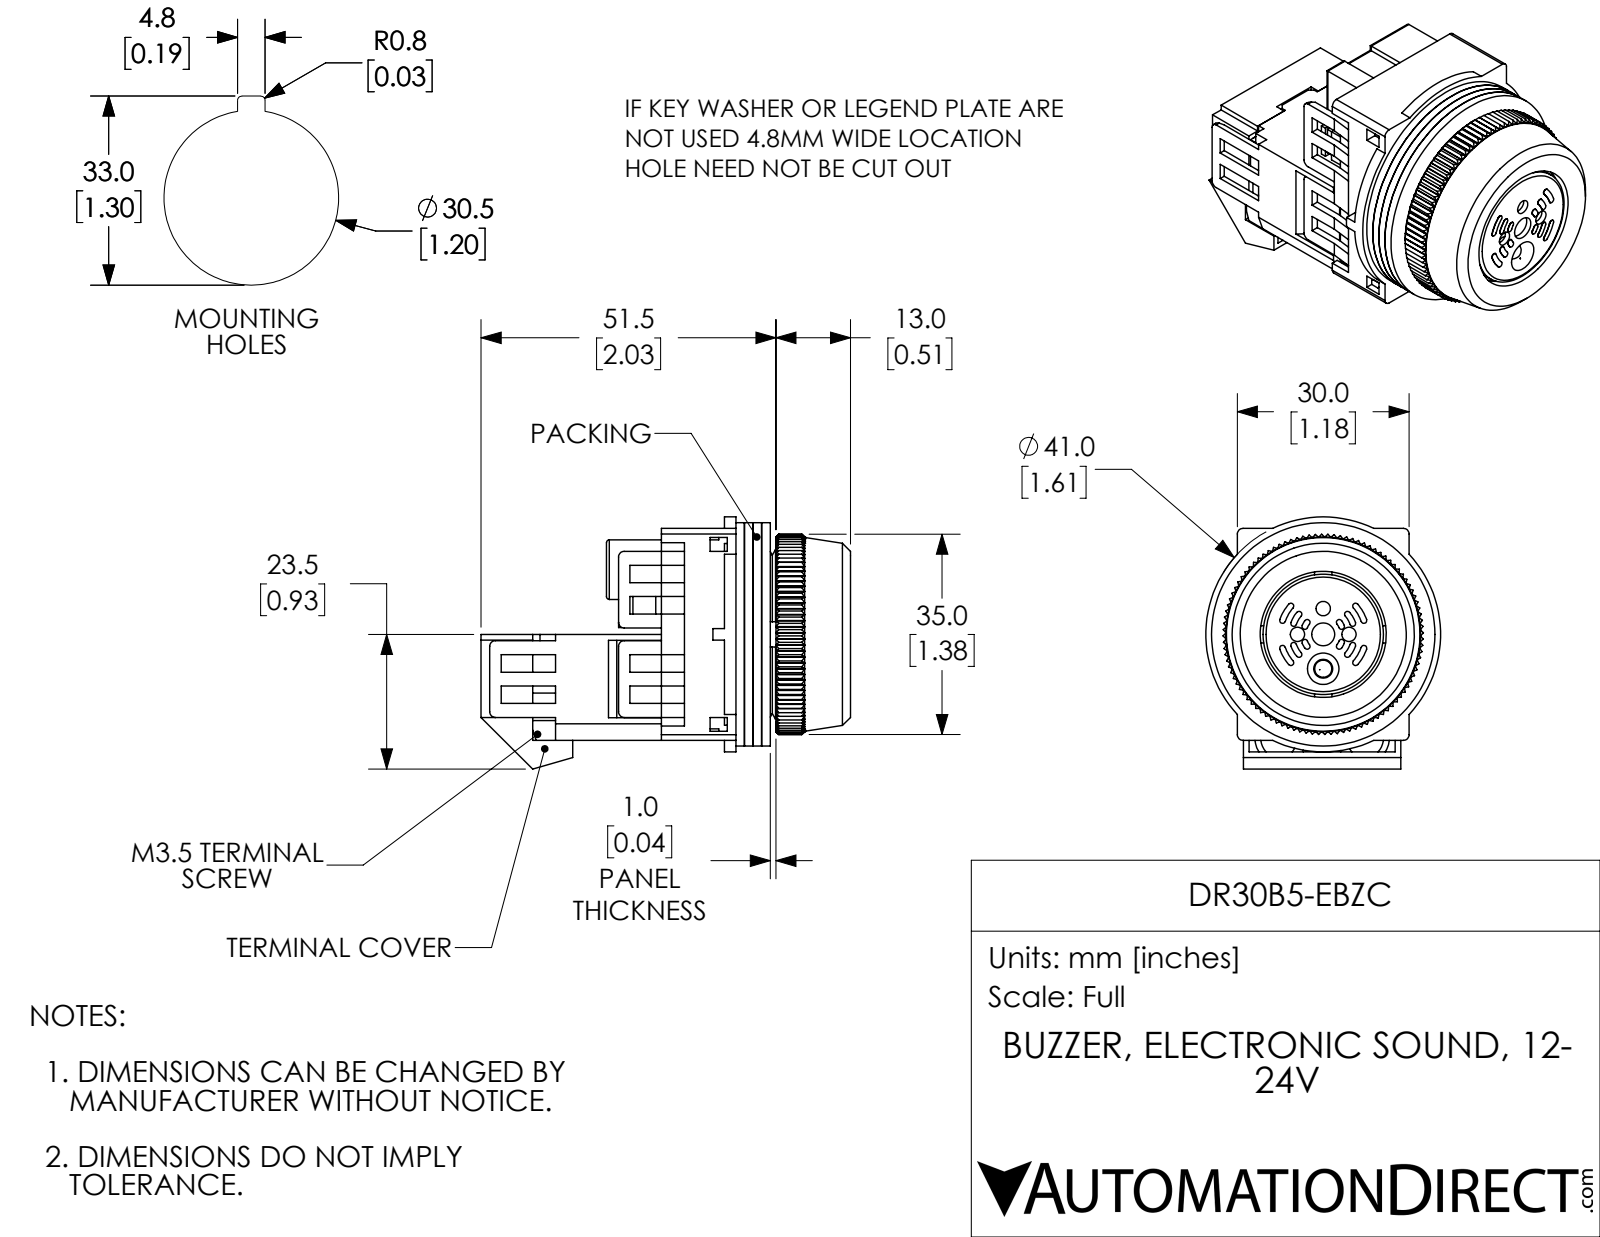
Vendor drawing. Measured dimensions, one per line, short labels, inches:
name: DR30B5-EBZC
written by: SolidWorks 2024 (CONFIG_CONTROL_DESIGN)
unit: in
bodies: 18 solids, 1273 faces (854 planar, 315 cylindrical, 104 other)
size: 2.539 × 1.732 × 1.614
volume: 2.084 in³; area: 48.26 in²
holes: 3× ⌀0.098, 3× ⌀0.138, 2× ⌀0.118, 2× ⌀0.142, 1× ⌀0.157, 1× ⌀0.709, 1× ⌀0.866, 1× ⌀1.114, 1× ⌀1.173
bosses: 2× ⌀0.26, 2× ⌀0.138, 1× ⌀1.614, 1× ⌀1.535, 1× ⌀1.181, 1× ⌀1.181, 1× ⌀1.102, 1× ⌀0.827
rounds: 31× R0.02, 12× R0.039, 8× R0.059, 2× R0.118, 1× R0.029, 1× R0.063, 1× R0.068, 1× R0.157
face distances: 0.059, 0.118, 0.039, 0.177, 0.689, 0.079, 0.354, 0.571, 0.512, 0.728
hole spacings: 0.177, 0.25, 0.354, 0.472, 0.502, 0.507, 0.591, 0.65
